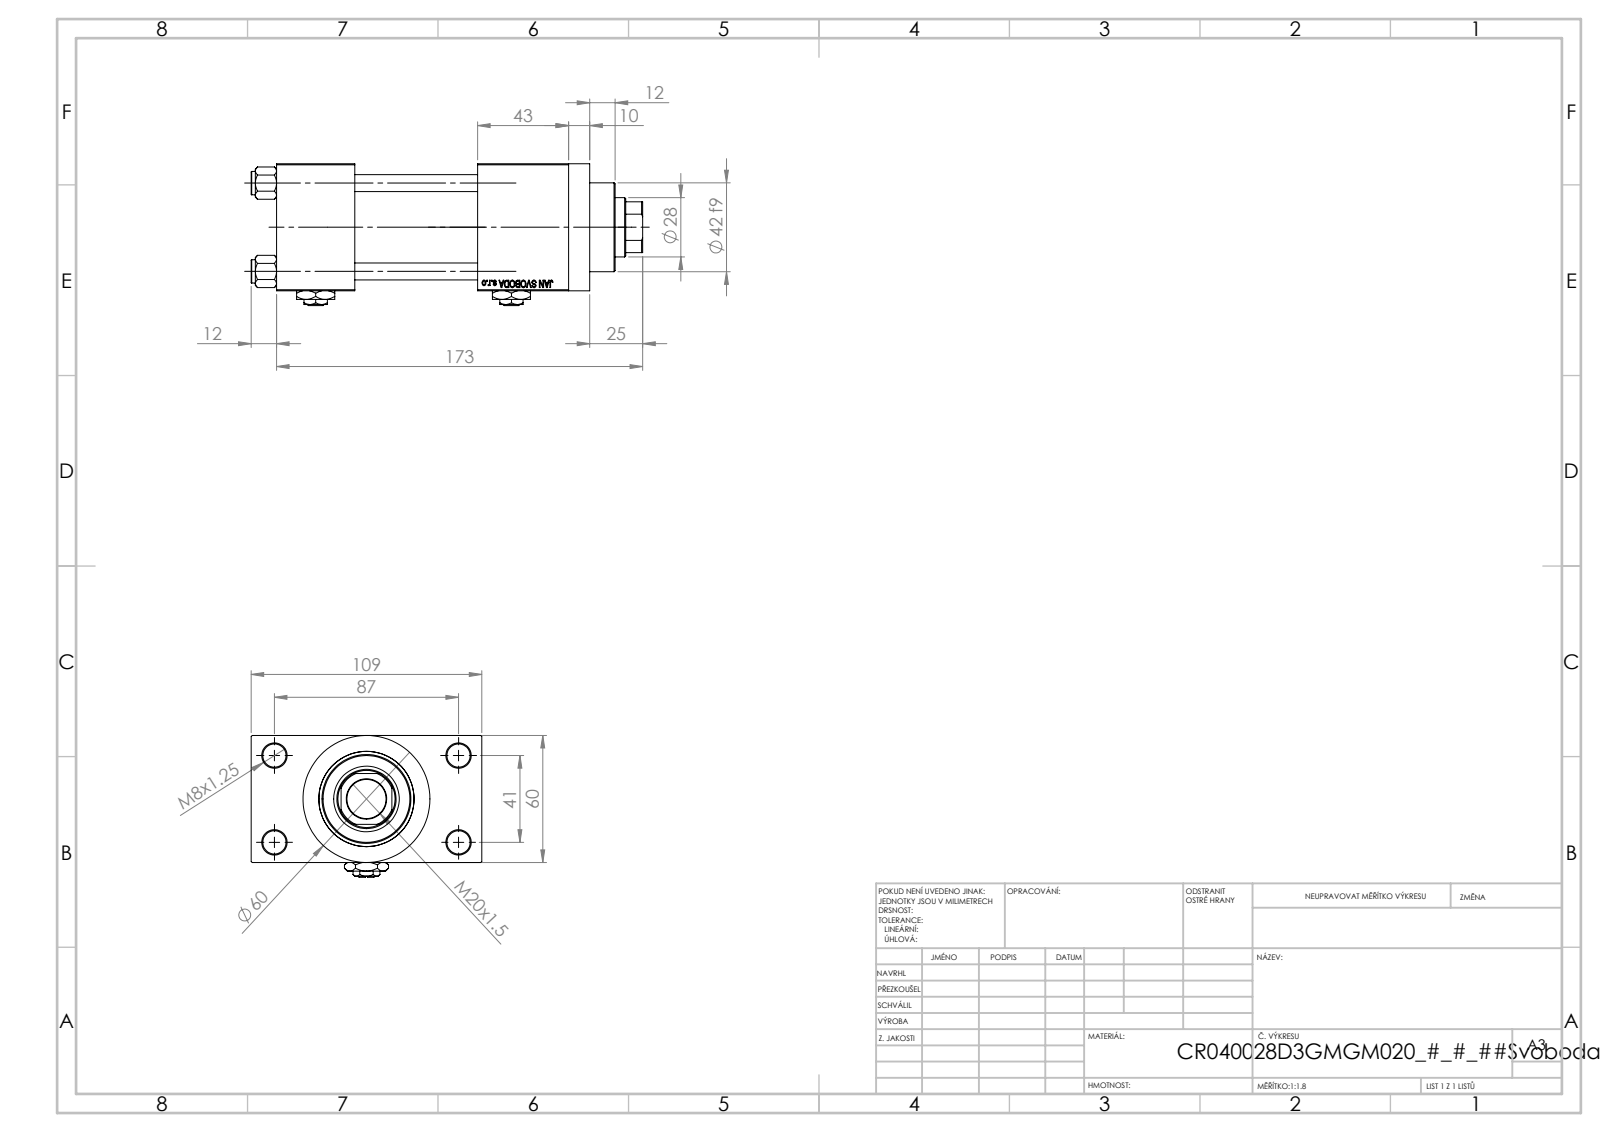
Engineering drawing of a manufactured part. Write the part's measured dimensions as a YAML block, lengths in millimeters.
part_name: "NUT_M5_D; V215CR_D_Body; V215CR_D_TYCINKA; Zatka_pro_OIL_PORT (+2 more)"
step_written_by: "SolidWorks 2019 (CONFIG_CONTROL_DESIGN)"
units: millimeters
bodies: {solids: 13, faces: 1205, planar: 546, cylindrical: 99, other: 560}
overall_size: [185, 109, 67]
volume: 527015
surface_area: 131664
round_holes:
  - {diameter: 8, count: 4}
  - {diameter: 11, count: 4}
  - {diameter: 16.66, count: 4}
  - {diameter: 24, count: 4}
  - {diameter: 7, count: 3}
  - {diameter: 18.5, count: 1}
  - {diameter: 28, count: 1}
  - {diameter: 31, count: 1}
  - {diameter: 40, count: 1}
  - {diameter: 45, count: 1}
round_bosses_or_shafts:
  - {diameter: 11, count: 4}
  - {diameter: 60, count: 1}
  - {diameter: 46, count: 1}
  - {diameter: 42, count: 1}
partial_cylinders:
  - {radius: 13.5, count: 1}
face_to_face_distances: [60, 58, 24.5, 84.5, 37, 95, 138, 101, 43, 109]
hole_center_spacings: [22.65, 29.49, 41.7, 47.15, 48.09, 64.35, 76.49, 41]
